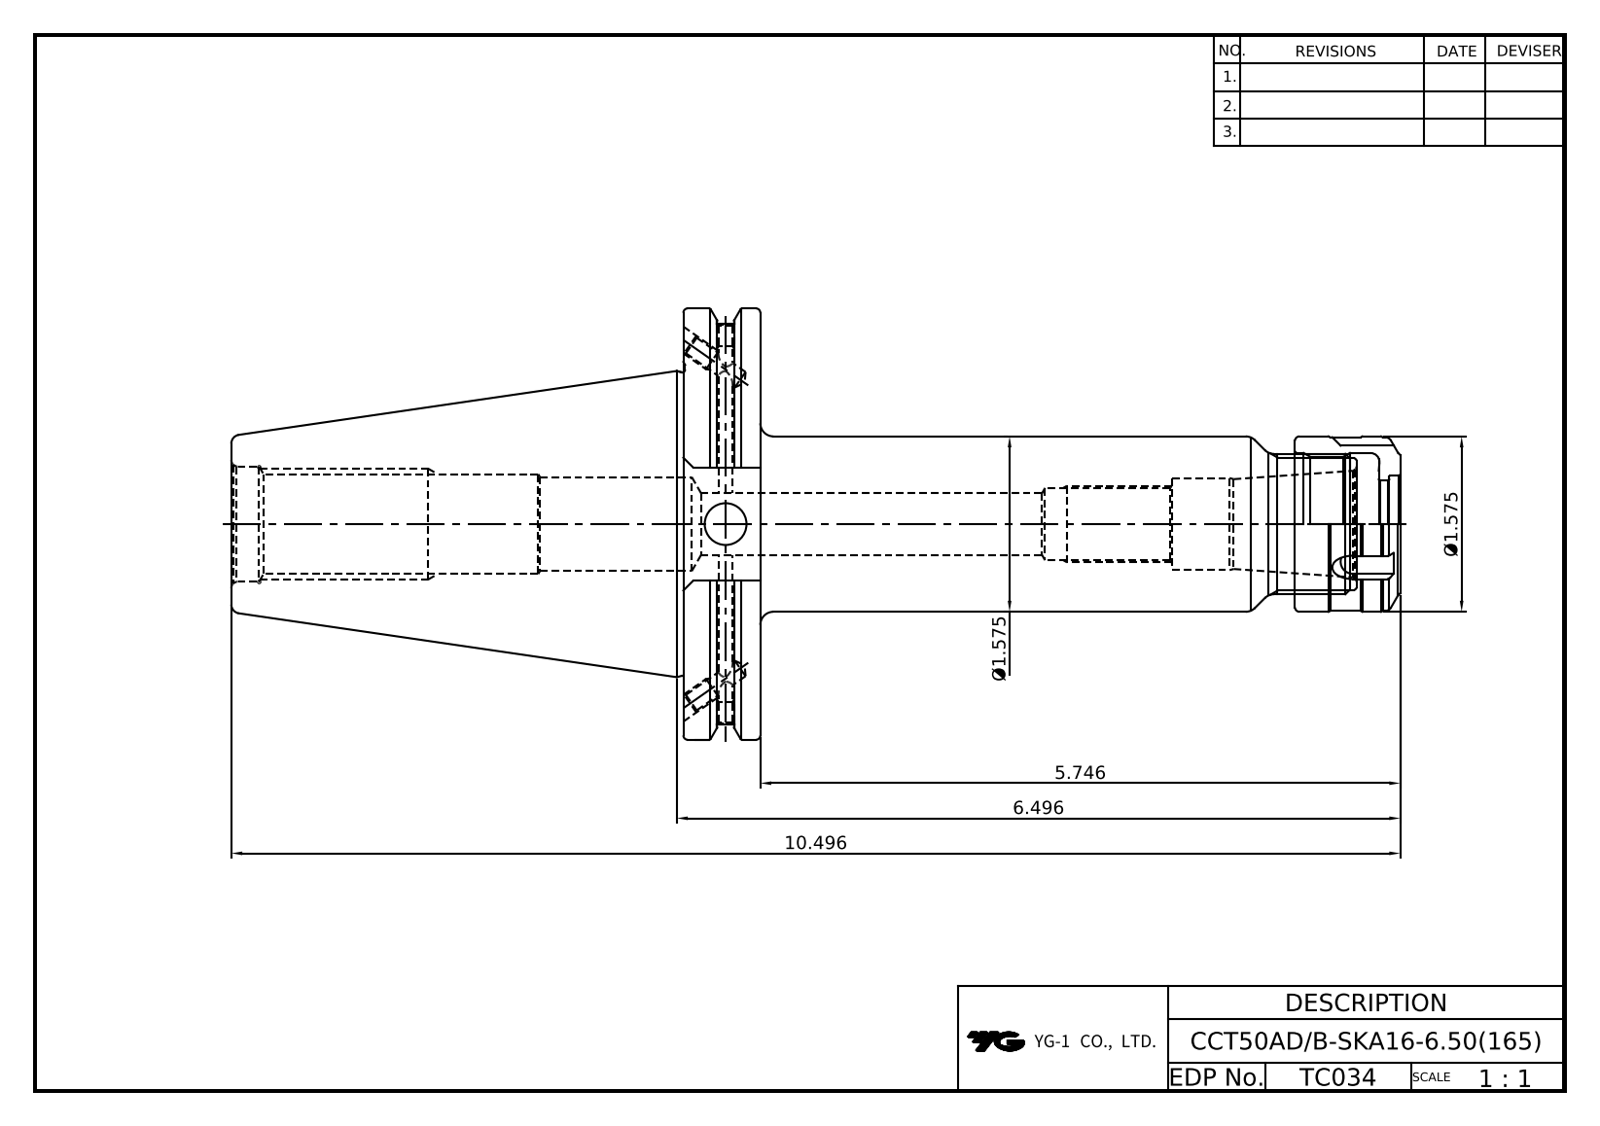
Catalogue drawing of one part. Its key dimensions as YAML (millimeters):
part_name: "LO-CCT50ADB-SKA16-165; SKN16-NUT"
step_written_by: "Autodesk Inventor 2022 (AUTOMOTIVE_DESIGN)"
units: millimeters
bodies: {solids: 2, faces: 166, planar: 59, cylindrical: 48, other: 59}
overall_size: [266.6, 98.42, 94.69]
volume: 467726
surface_area: 75095
round_holes:
  - {diameter: 3.24, count: 2}
  - {diameter: 4.13, count: 2}
  - {diameter: 4.2, count: 2}
  - {diameter: 5, count: 2}
  - {diameter: 9.53, count: 1}
  - {diameter: 14, count: 1}
  - {diameter: 15.75, count: 1}
  - {diameter: 19.8, count: 1}
  - {diameter: 21, count: 1}
  - {diameter: 21.5, count: 1}
  - {diameter: 21.97, count: 1}
  - {diameter: 22, count: 1}
round_bosses_or_shafts:
  - {diameter: 98.42, count: 1}
  - {diameter: 91.29, count: 1}
  - {diameter: 69.25, count: 1}
  - {diameter: 40, count: 1}
  - {diameter: 39.6, count: 1}
  - {diameter: 29.98, count: 1}
face_to_face_distances: [17.55, 103.1, 120.65, 261.7, 158.6, 141.05, 266.6, 163.5, 145.95, 4.9]
